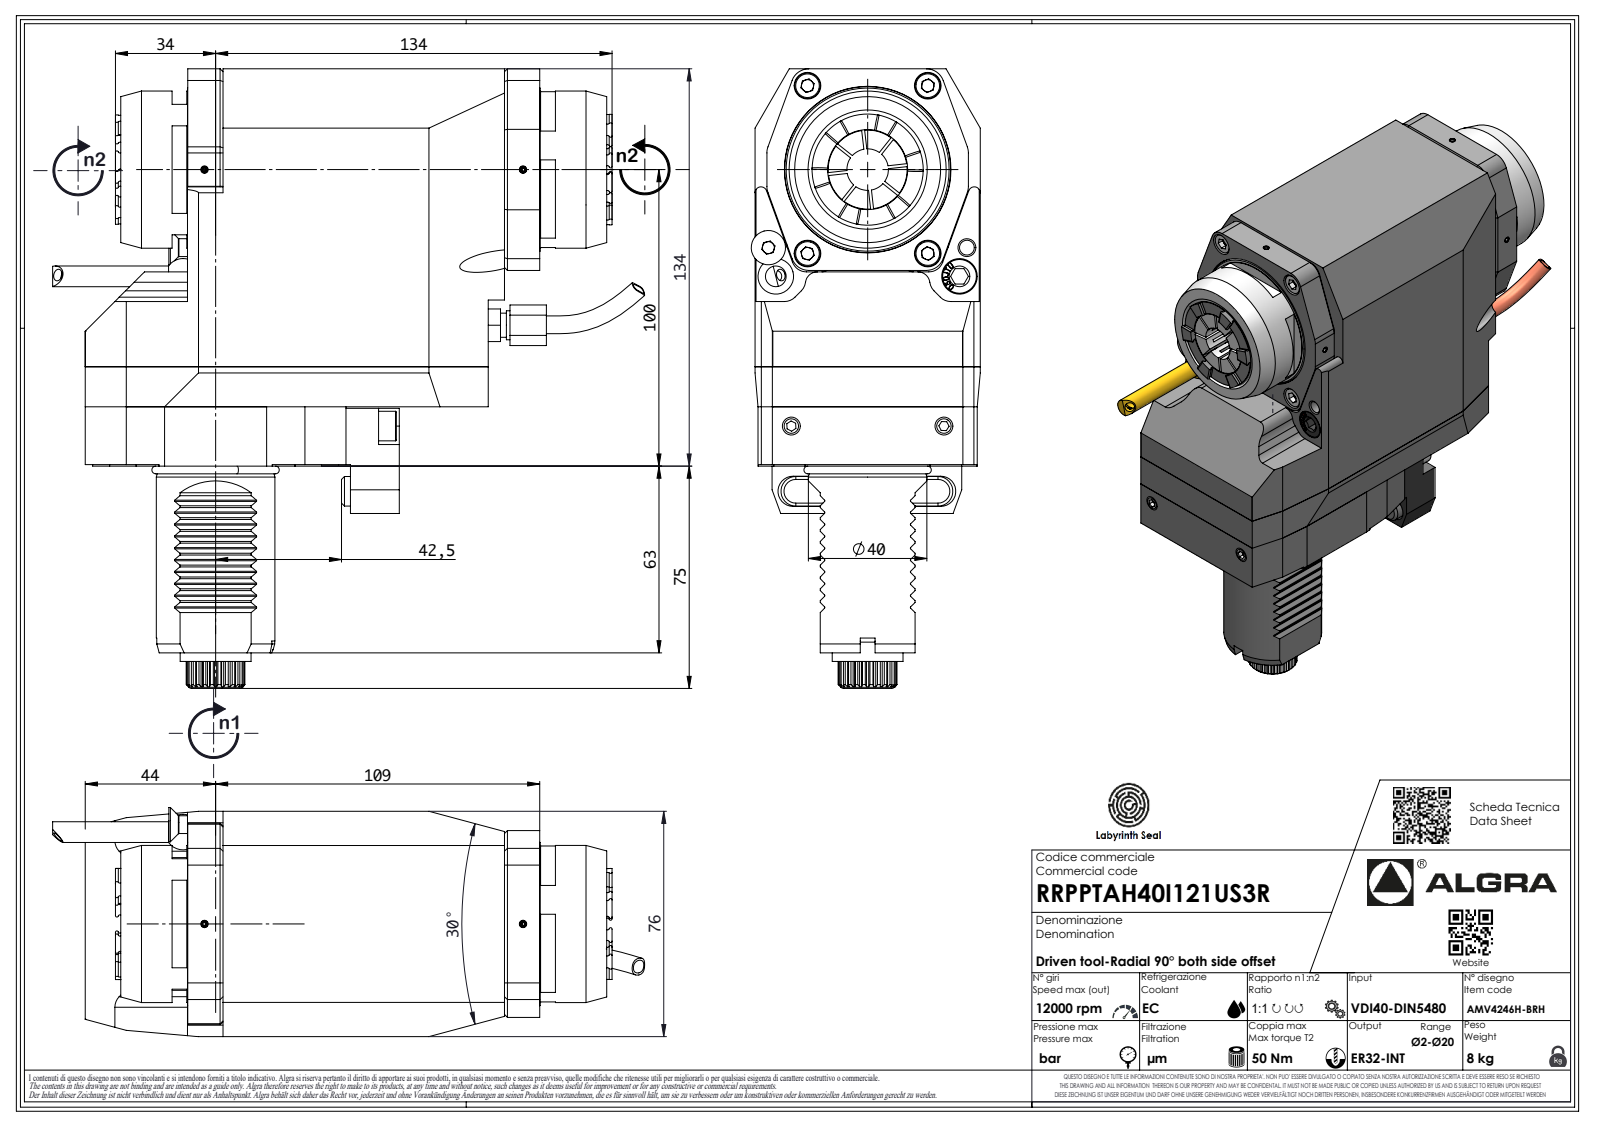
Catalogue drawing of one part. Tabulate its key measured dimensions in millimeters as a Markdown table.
| quantity | value |
| --- | --- |
| part name | RRPPTAH40I121US3R |
| STEP written by | SolidWorks 2023 (AUTOMOTIVE_DESIGN) |
| units | millimeters |
| bodies | 1 solid, 740 faces (516 planar, 122 cylindrical, 102 other) |
| overall size | 209 × 199.81 × 76 |
| volume | 1 328 000 mm³ |
| surface area | 96 389 mm² |
| round holes (diameter × count) | 2.05 × 1, 2.1 × 1, 4 × 1, 30.4 × 1 |
| round bosses / shafts (diameter × count) | 53 × 1, 40 × 1, 38.7 × 1, 17.5 × 1, 9.8 × 1, 8.15 × 1, 7 × 1, 6.37 × 1 |
| partial cylindrical surfaces (radius × count) | 0.3 × 20, 6 × 10, 0.33 × 7, 0.52 × 7, 3.7 × 7, 5 × 6, 3 × 5, 2 × 3 |
| main face-to-face distances | 76, 0.5, 12, 134, 20, 114, 19.5, 22.6, 141.4, 133.5 |
| hole center spacings | 16.9 |
